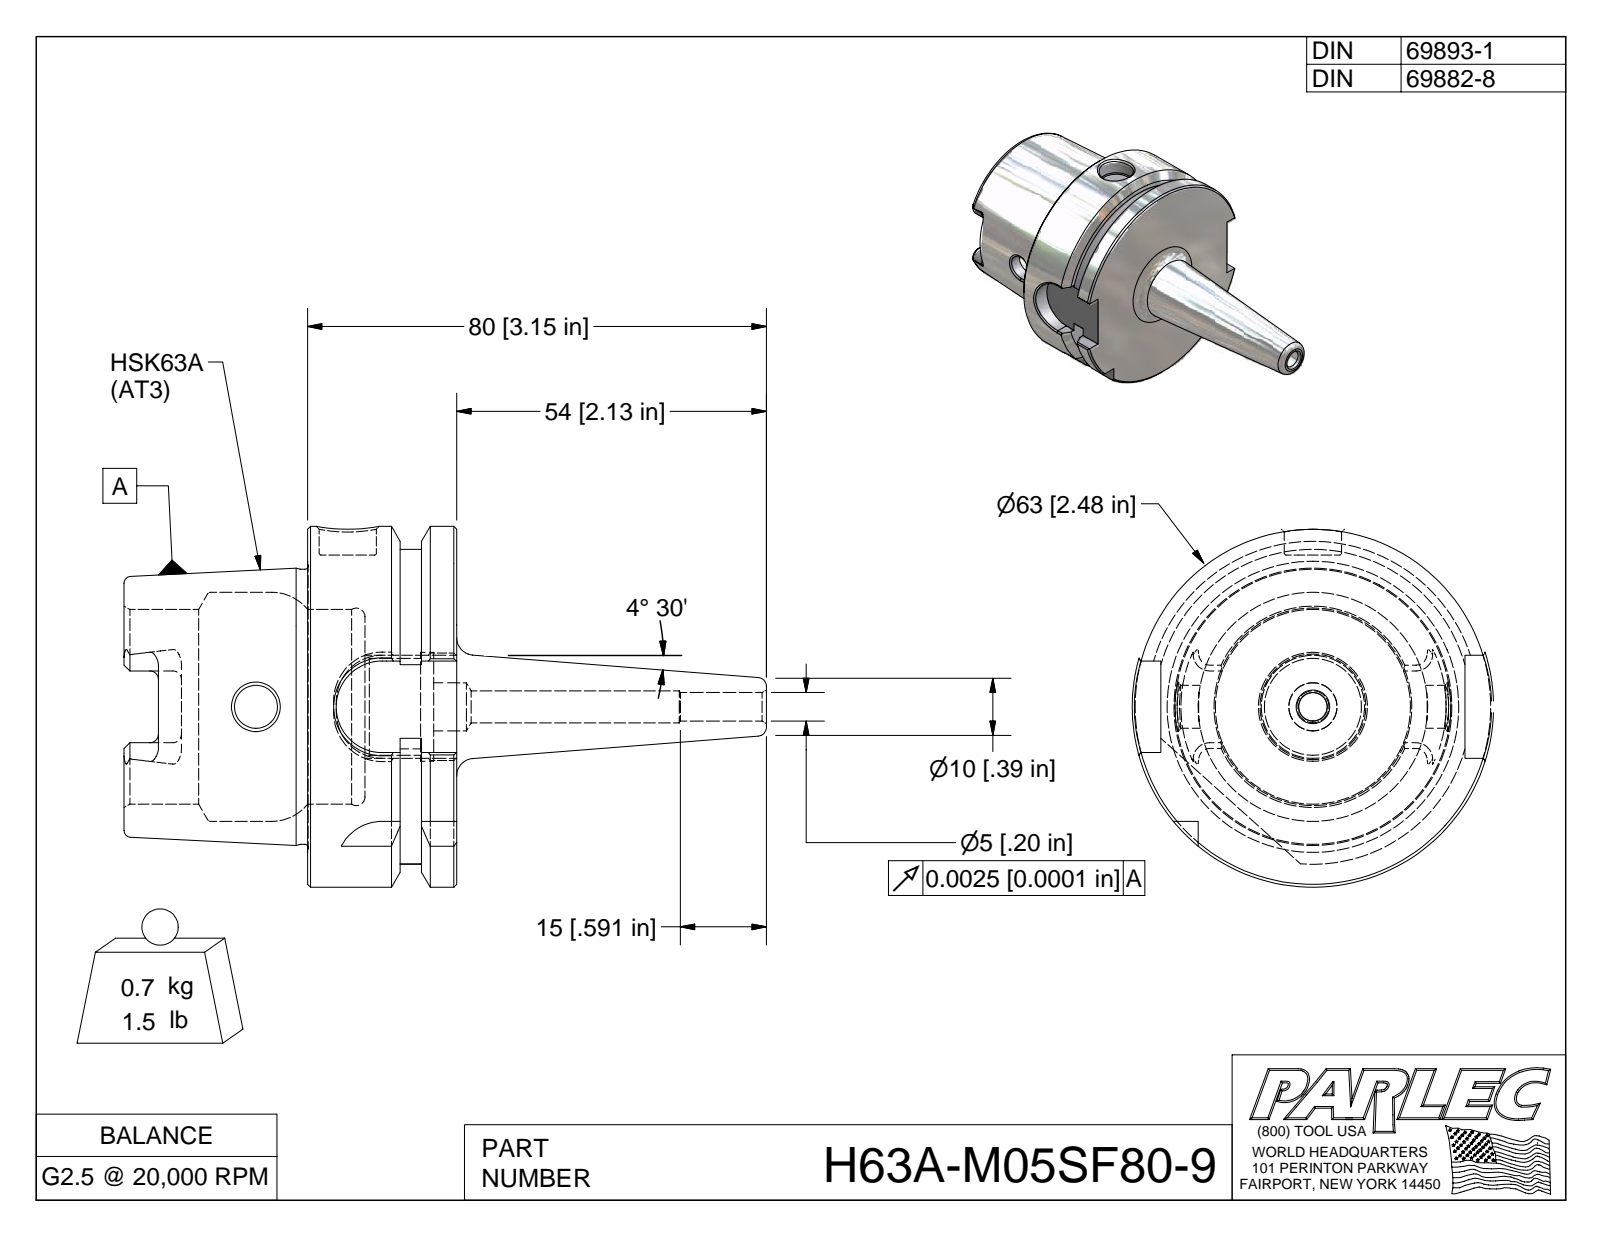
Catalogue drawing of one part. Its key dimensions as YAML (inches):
part_name: "H63A-M05SF80-9; H63A-M05SF80-9-1"
step_written_by: "Autodesk Inventor 2009 (AUTOMOTIVE_DESIGN)"
units: inches
bodies: {solids: 1, faces: 138, planar: 48, cylindrical: 33, other: 57}
overall_size: [4.409, 2.48, 2.48]
volume: 5.413
surface_area: 39.77
round_holes:
  - {diameter: 0.196, count: 1}
  - {diameter: 0.295, count: 1}
  - {diameter: 0.331, count: 1}
  - {diameter: 0.394, count: 1}
  - {diameter: 0.666, count: 1}
  - {diameter: 0.749, count: 1}
  - {diameter: 1.339, count: 1}
  - {diameter: 1.575, count: 1}
round_bosses_or_shafts:
  - {diameter: 2.48, count: 1}
  - {diameter: 1.891, count: 1}
partial_cylinders:
  - {radius: 0.059, count: 6}
  - {radius: 0.113, count: 4}
  - {radius: 0.315, count: 4}
  - {radius: 1.083, count: 1}
face_to_face_distances: [1.024, 0.241, 0.389, 0.394, 0.63, 1.26, 2.283, 1.654, 1.894, 0.635]
